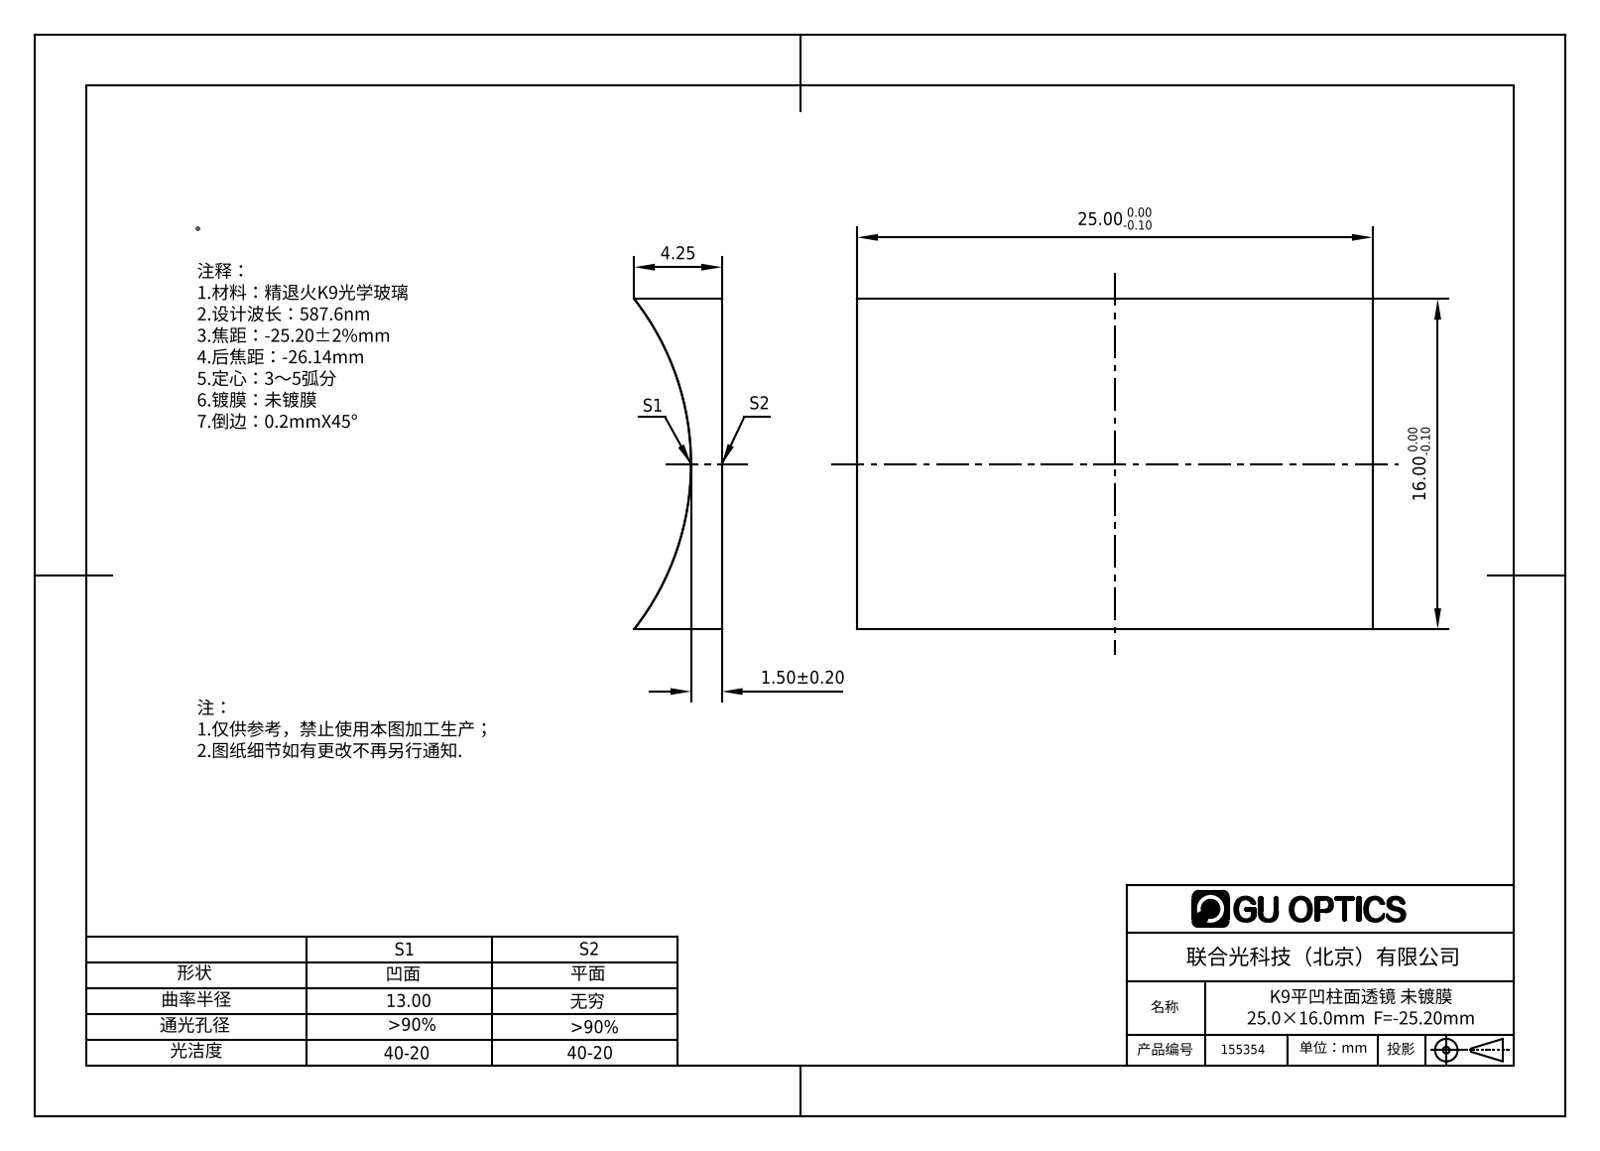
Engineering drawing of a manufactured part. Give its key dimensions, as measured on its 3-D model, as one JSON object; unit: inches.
{"part_name": "155354", "step_written_by": "SolidWorks 2016 (AUTOMOTIVE_DESIGN)", "units": "inches", "bodies": {"solids": 1, "faces": 6, "planar": 5, "cylindrical": 1, "other": 0}, "overall_size": [0.984, 0.63, 0.167], "volume_in3": 0.058, "surface_area_in2": 1.736, "partial_cylinders_radius": [[0.512, 1]], "face_to_face_distances": [0.63, 0.984]}
